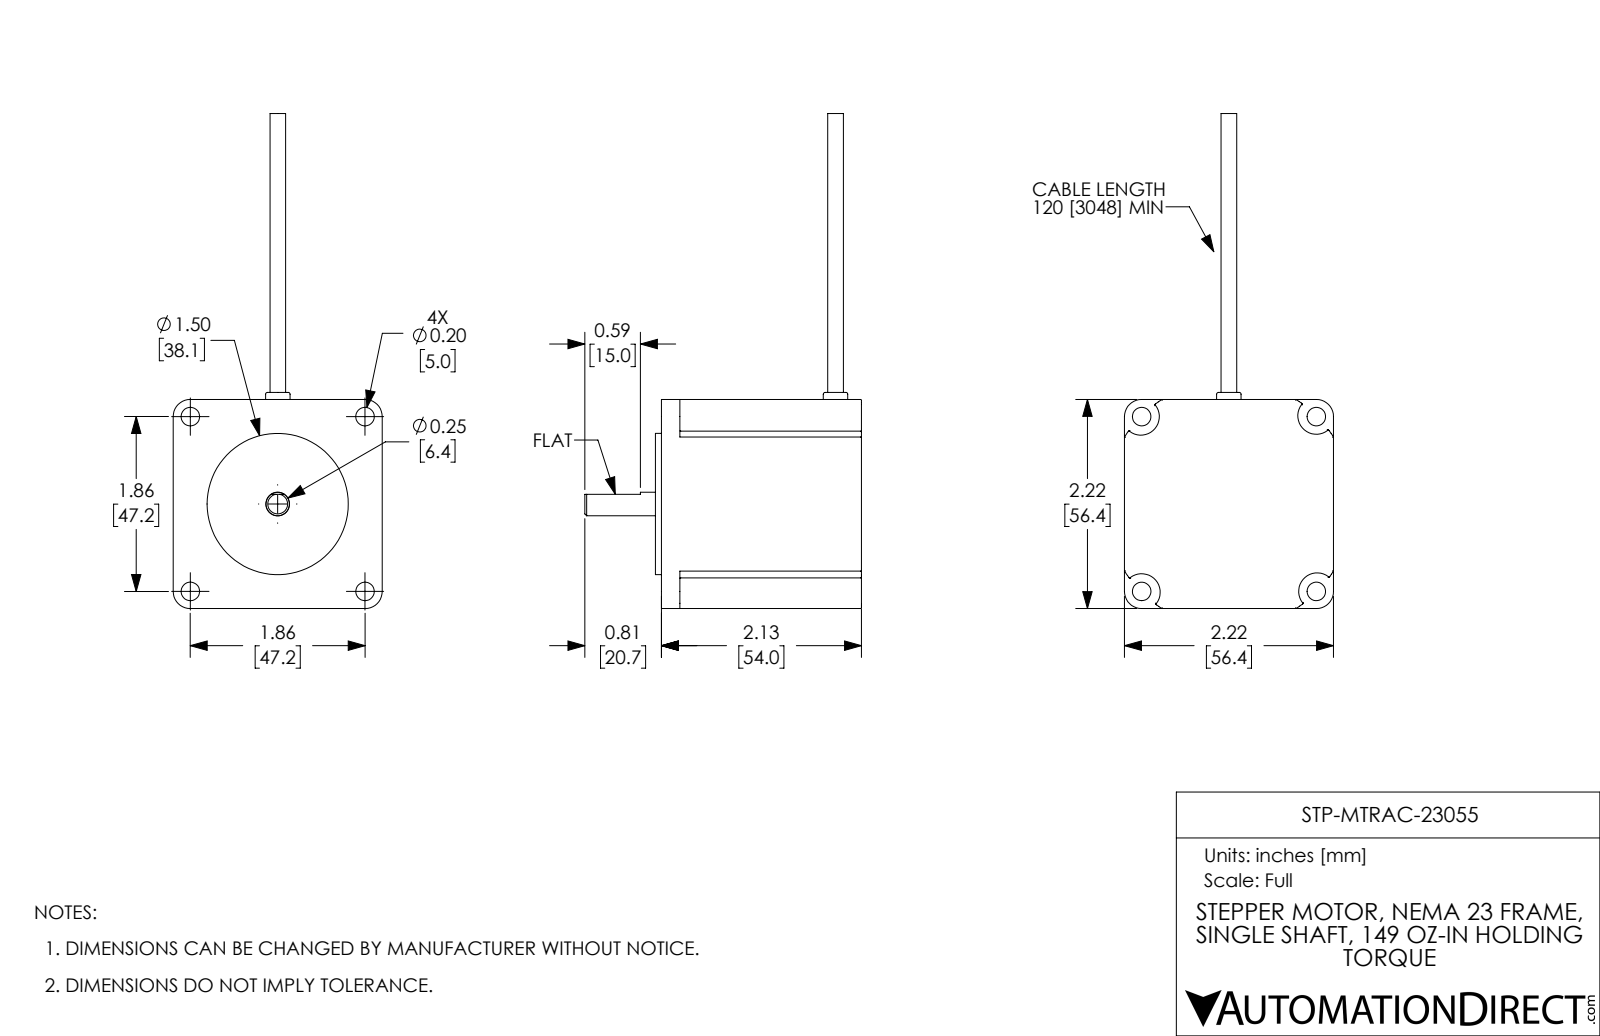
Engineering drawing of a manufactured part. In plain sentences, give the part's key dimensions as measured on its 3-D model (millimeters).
The part is named "STP-MTRAC-23055 from HT23-553-CAA r1". Its 3-D file was written by "SolidWorks 2017 (AUTOMOTIVE_DESIGN)". It is 1 solid with 125 faces: 16 planar, 48 cylindrical and 61 other. Overall it measures 133.5 by 74.65 by 56.4 millimeters. Its volume is 158 771 cubic millimeters and its surface area 19 987 square millimeters. Round holes: 4 of diameter 5. Round bosses or shafts: 1 of diameter 38.1, 1 of diameter 6.58, 1 of diameter 6.35, 1 of diameter 4.23. Partial cylindrical surfaces (rounded edges, fillets, slot ends): 12 of radius 0.25, 4 of radius 4.6, 4 of radius 5, 1 of radius 33.5. The main face-to-face distances are 56.4, 54, 55.6, 1.6, 49, 5, 6.6, 30.82, 25.58, 74.65. The hole center spacings are 47.14, 66.67.
